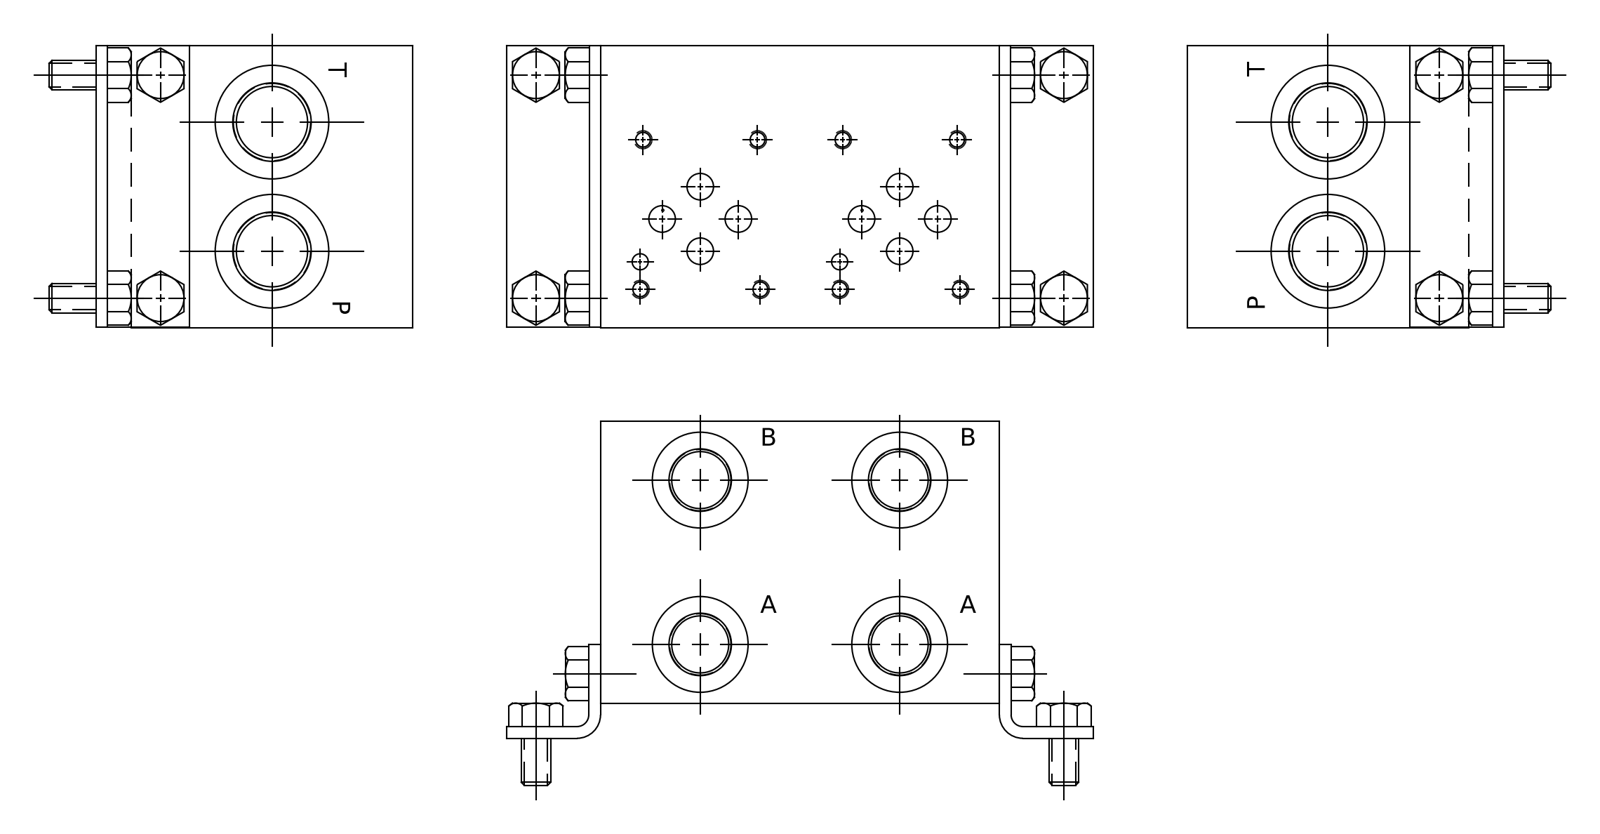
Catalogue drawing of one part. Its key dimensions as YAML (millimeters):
part_name: "Part_AD03P022B_3D"
step_written_by: "Autodesk Inventor 2022 (AUTOMOTIVE_DESIGN)"
units: millimeters
bodies: {solids: 1, faces: 587, planar: 336, cylindrical: 66, other: 185}
overall_size: [107.95, 76.2, 76.2]
volume: 568770
surface_area: 59496
round_holes:
  - {diameter: 4.22, count: 8}
  - {diameter: 5, count: 8}
  - {diameter: 7.14, count: 6}
  - {diameter: 14.3, count: 4}
  - {diameter: 15.06, count: 4}
  - {diameter: 16.76, count: 4}
  - {diameter: 25.93, count: 4}
  - {diameter: 3.96, count: 2}
  - {diameter: 6.35, count: 2}
  - {diameter: 6.76, count: 2}
  - {diameter: 8, count: 2}
  - {diameter: 15.88, count: 2}
face_to_face_distances: [76.2, 107.95, 0.79, 107.16, 75.41, 106.37, 16.59, 91.36, 15.8, 90.57]
hole_center_spacings: [53.98, 53.97, 19.95, 22.05, 33.55, 40.49, 51.45, 7.49]
